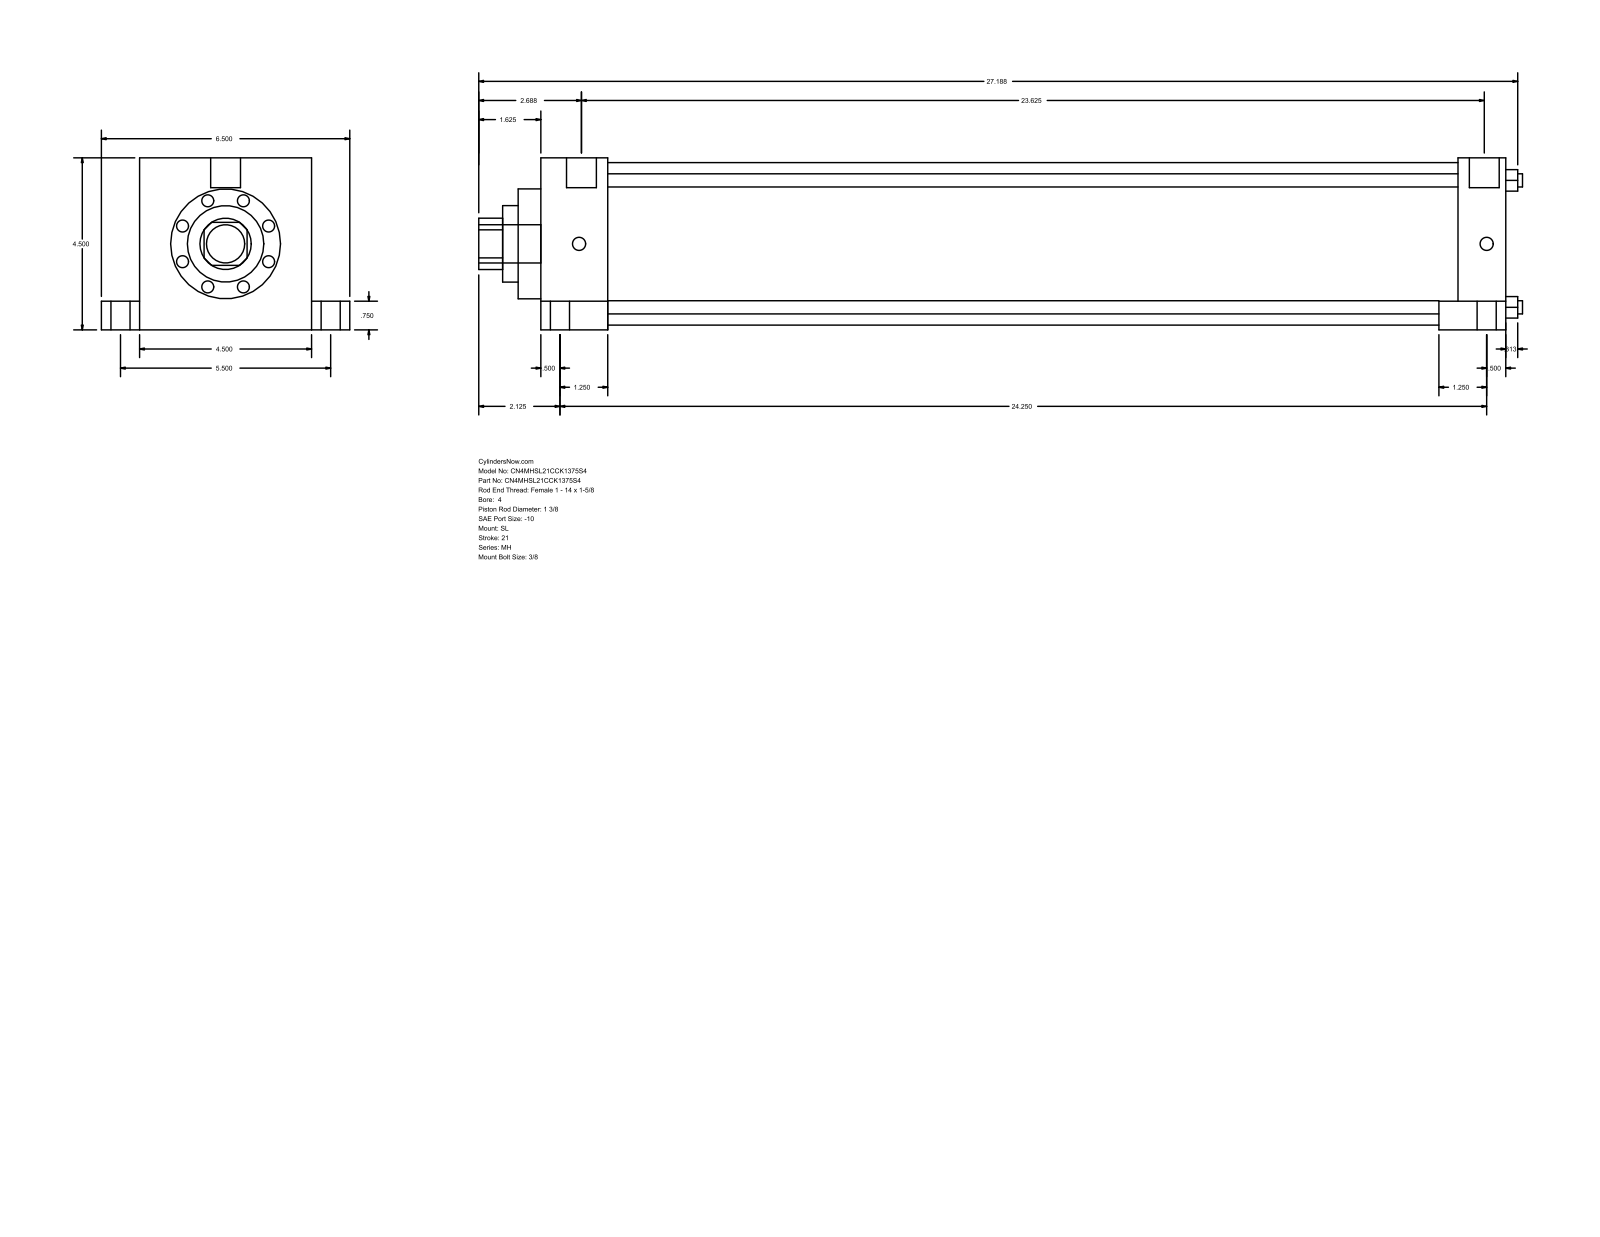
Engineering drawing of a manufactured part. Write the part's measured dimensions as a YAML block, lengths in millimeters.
part_name: "MH_SL__0400_1.375"
step_written_by: "GSSL Pune (CONFIG_CONTROL_DESIGN)"
units: millimeters
bodies: {solids: 0, faces: 110, planar: 77, cylindrical: 33, other: 0}
overall_size: [693.74, 165.1, 114.3]
round_holes:
  - {diameter: 8.76, count: 4}
  - {diameter: 34.92, count: 1}
  - {diameter: 50.8, count: 1}
  - {diameter: 73.03, count: 1}
  - {diameter: 107.95, count: 1}
round_bosses_or_shafts:
  - {diameter: 19.05, count: 4}
  - {diameter: 12.7, count: 4}
  - {diameter: 8.73, count: 4}
  - {diameter: 19.84, count: 2}
  - {diameter: 25.4, count: 1}
partial_cylinders:
  - {radius: 17.06, count: 1}
face_to_face_distances: [114.3, 641.35, 44.45, 596.9, 609.61, 565.16, 31.74, 25.4, 139.7, 19.05]
hole_center_spacings: [59.62, 84.32, 119.25]
